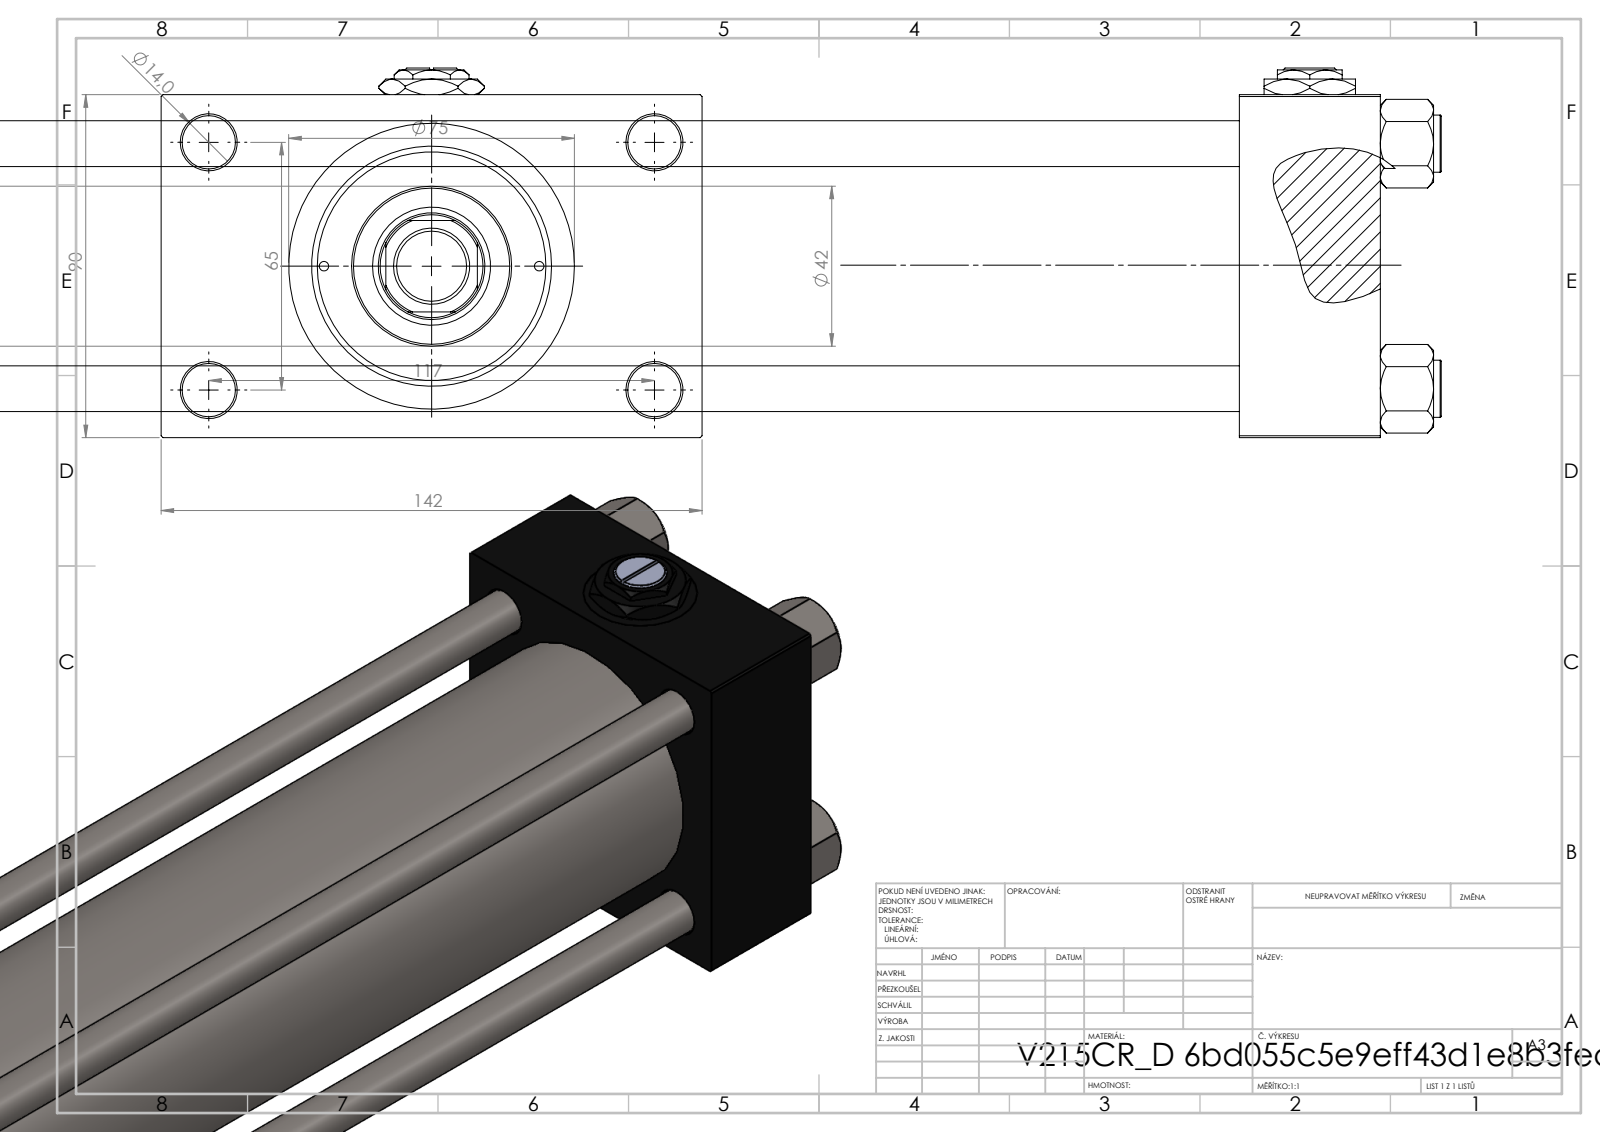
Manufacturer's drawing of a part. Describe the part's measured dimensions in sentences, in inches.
The part is named "NUT_M5_D; V215CR_VCP_D; V215CR_D_TYCINKA; V215CR_D_Body (+3 more)". Its 3-D file was written by "SolidWorks 2019 (CONFIG_CONTROL_DESIGN)". It is 14 solids with 1226 faces: 551 planar, 107 cylindrical and 568 other. Overall it measures 20.118 by 5.591 by 3.819 inches. Its volume is 95.93 cubic inches and its surface area 604.9 square inches. Round holes: 4 of diameter 0.472, 4 of diameter 0.551, 4 of diameter 0.825, 4 of diameter 1.181, 3 of diameter 0.276, 2 of diameter 0.098, 1 of diameter 0.728, 1 of diameter 1.102, 1 of diameter 1.22, 1 of diameter 1.969, 1 of diameter 2.362, 1 of diameter 2.48. Round bosses or shafts: 4 of diameter 0.591, 1 of diameter 2.953, 1 of diameter 2.717, 1 of diameter 1.654, 1 of diameter 0.787, 1 of diameter 0.709. Partial cylindrical surfaces (rounded edges, fillets, slot ends): 1 of radius 0.531. The main face-to-face distances are 3.543, 13.346, 1.457, 14.803, 15.079, 16.535, 1.732, 1.024, 4.567, 0.63. The hole center spacings are 1.037, 1.275, 1.748, 1.79, 2.531, 2.635, 2.694, 2.748.
